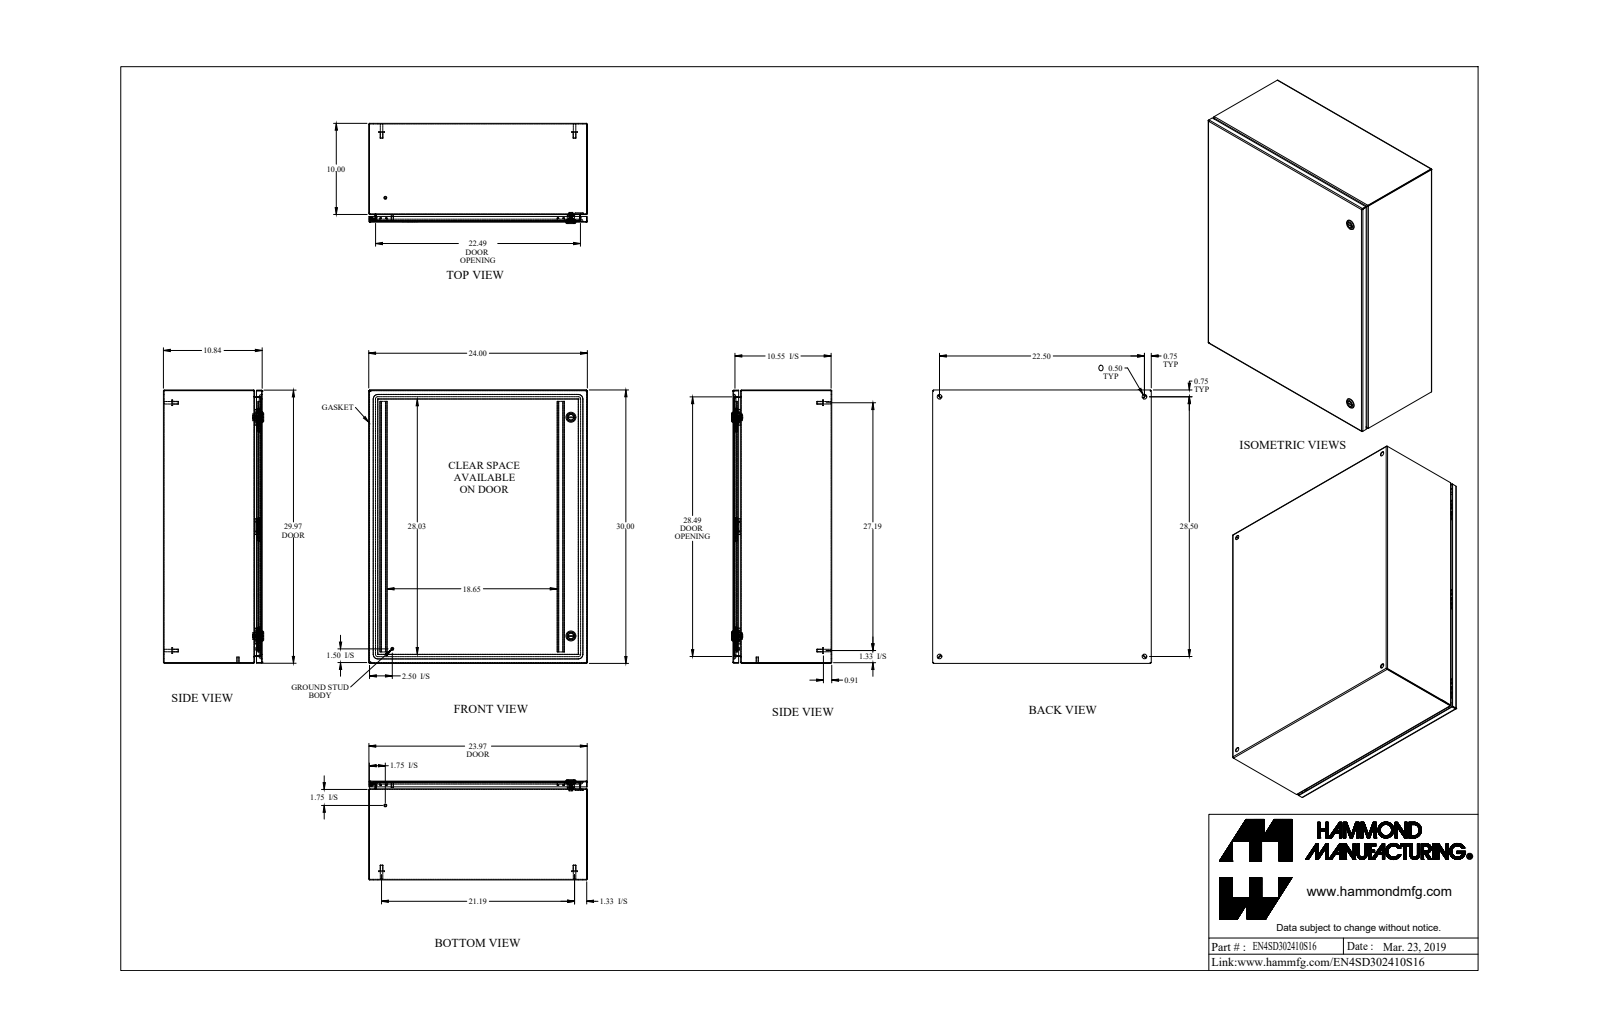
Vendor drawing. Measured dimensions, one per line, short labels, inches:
name: EN4SD302410S16
written by: SolidWorks 2019 (AUTOMOTIVE_DESIGN)
unit: in
bodies: 33 solids, 891 faces (423 planar, 300 cylindrical, 168 other)
size: 30 × 24 × 11.002
volume: 211 in³; area: 5 924 in²
holes: 6× ⌀0.5, 2× ⌀0.197, 2× ⌀0.387, 2× ⌀0.63, 2× ⌀0.768, 1× ⌀0.172, 1× ⌀0.24, 1× ⌀0.242
bosses: 6× ⌀0.625, 6× ⌀0.313, 4× ⌀0.275, 2× ⌀1.1, 2× ⌀0.785, 2× ⌀0.525, 2× ⌀0.25, 2× ⌀0.236
rounds: 16× R0.036, 16× R0.108, 16× R0.25, 12× R0.01, 12× R0.048, 8× R0.1, 6× R0.006, 6× R0.062
face distances: 0.072, 10.77, 10.698, 10.842, 23.928, 29.928, 23.856, 24, 29.856, 30
hole spacings: 2.488, 21.557, 22.5, 26.271, 28.5, 33.893, 36.311, 24
